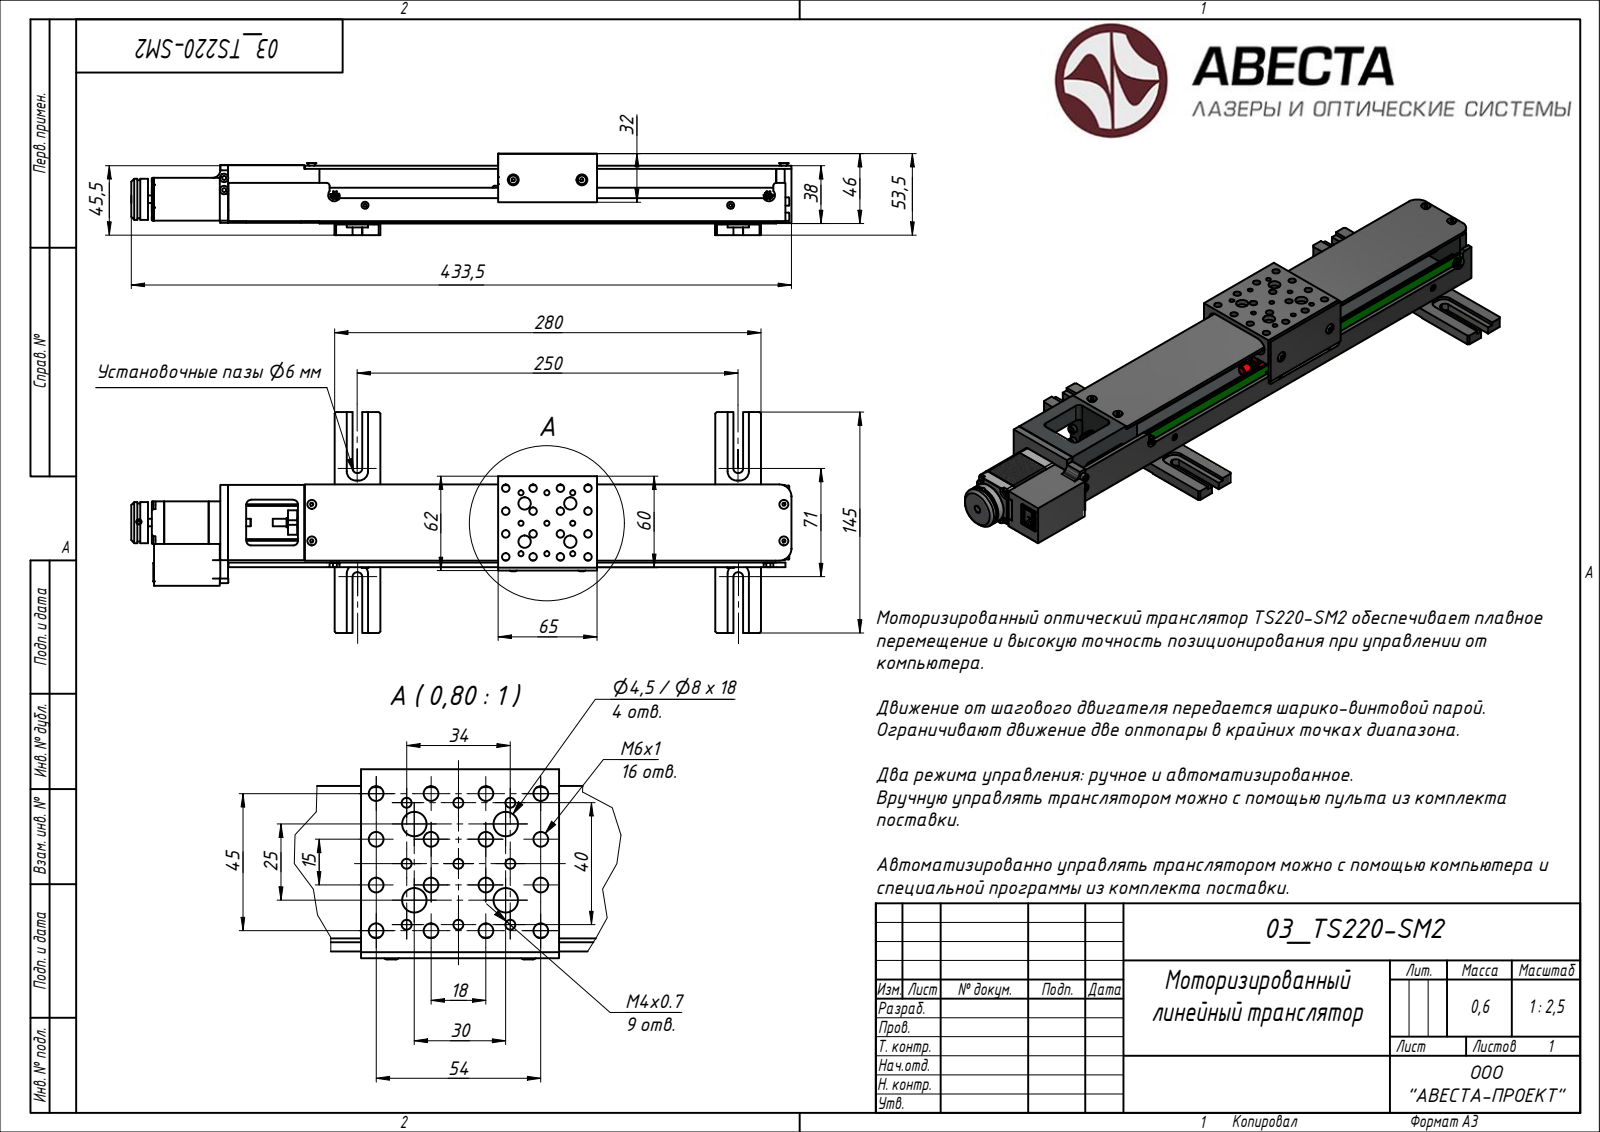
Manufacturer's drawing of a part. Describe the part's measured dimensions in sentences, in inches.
Its 3-D file was written by "Rhino 7.34 (AUTOMOTIVE_DESIGN)". It is 1 solid with 1330 faces: 723 planar, 386 cylindrical and 221 other. Overall it measures 17.067 by 5.709 by 2.106 inches. Its volume is 28.02 cubic inches and its surface area 301.3 square inches. Round holes: 13 of diameter 0.128, 12 of diameter 0.315, 9 of diameter 0.194, 6 of diameter 0.087, 6 of diameter 0.134, 5 of diameter 0.041, 4 of diameter 0.063, 4 of diameter 0.081, 4 of diameter 0.177, 3 of diameter 0.097, 2 of diameter 0.097, 2 of diameter 0.098. Round bosses or shafts: 12 of diameter 0.217, 8 of diameter 0.276, 7 of diameter 0.236, 5 of diameter 0.118, 2 of diameter 0.177, 2 of diameter 0.098, 1 of diameter 1.063, 1 of diameter 0.941. Partial cylindrical surfaces (rounded edges, fillets, slot ends): 16 of radius 0.118, 10 of radius 0.236, 8 of radius 0.098, 6 of radius 0.039, 6 of radius 0.079, 6 of radius 0.097, 6 of radius 0.097, 5 of radius 0.197. The main face-to-face distances are 0.079, 0.02, 0.295, 1.476, 0.315, 0.394, 0.256, 1.791, 1.398, 1.496. The hole center spacings are 1.033, 0.669, 0.709, 0.787, 1.682, 1.908, 0.039, 0.394.
